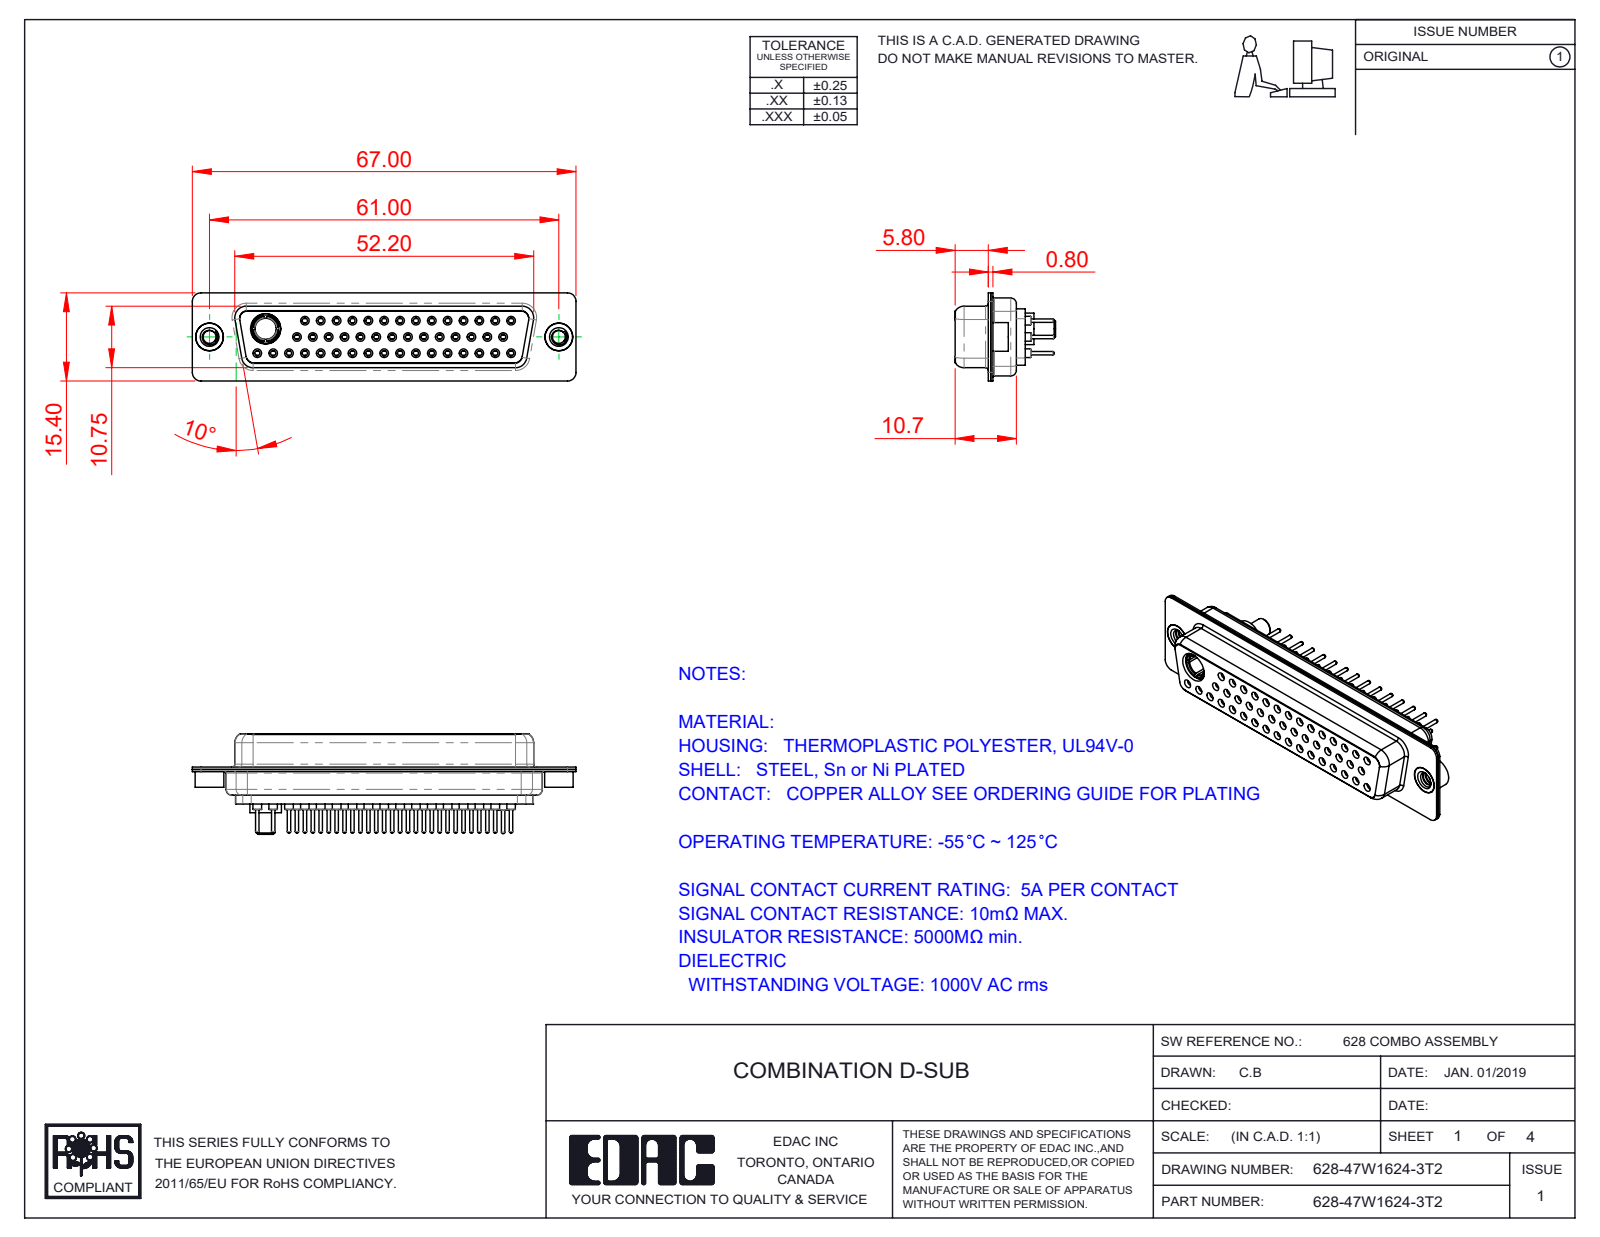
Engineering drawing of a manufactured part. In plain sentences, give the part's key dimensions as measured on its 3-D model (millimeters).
The part is named "628Combo Threaded Rivet_2; 628-47W1624-3T2; 628Combo Housing_47W1; 628Combo Shell Front_50 Contacts (+5 more)". Its 3-D file was written by "SolidWorks 2016 (CONFIG_CONTROL_DESIGN)". It is 53 solids with 2871 faces: 783 planar, 1026 cylindrical and 1062 other. Overall it measures 67 by 17.55 by 15.4 millimeters. Its volume is 7 093 cubic millimeters and its surface area 14 695 square millimeters. Round holes: 46 of diameter 1.1, 45 of diameter 0.9, 45 of diameter 1.5, 45 of diameter 2, 31 of diameter 1.6, 14 of diameter 1.7, 3 of diameter 4.85, 2 of diameter 2.26, 2 of diameter 4, 2 of diameter 4.05, 1 of diameter 3.7, 1 of diameter 5.3. Round bosses or shafts: 46 of diameter 2.2, 46 of diameter 0.6, 15 of diameter 1.6, 2 of diameter 5, 2 of diameter 4.95, 2 of diameter 4.8, 1 of diameter 5.5, 1 of diameter 5.2. Partial cylindrical surfaces (rounded edges, fillets, slot ends): 16 of radius 1.5, 12 of radius 1.35, 12 of radius 2, 8 of radius 1.6, 4 of radius 0.25, 4 of radius 0.5, 4 of radius 0.6, 4 of radius 0.65. The main face-to-face distances are 0.4, 11.33, 6.45, 6.05, 1.87, 12.25, 6.2, 5.8, 10.35, 10.93. The hole center spacings are 3.16, 2.77, 5.54, 8.31, 11.08, 13.85, 16.62, 19.39.
